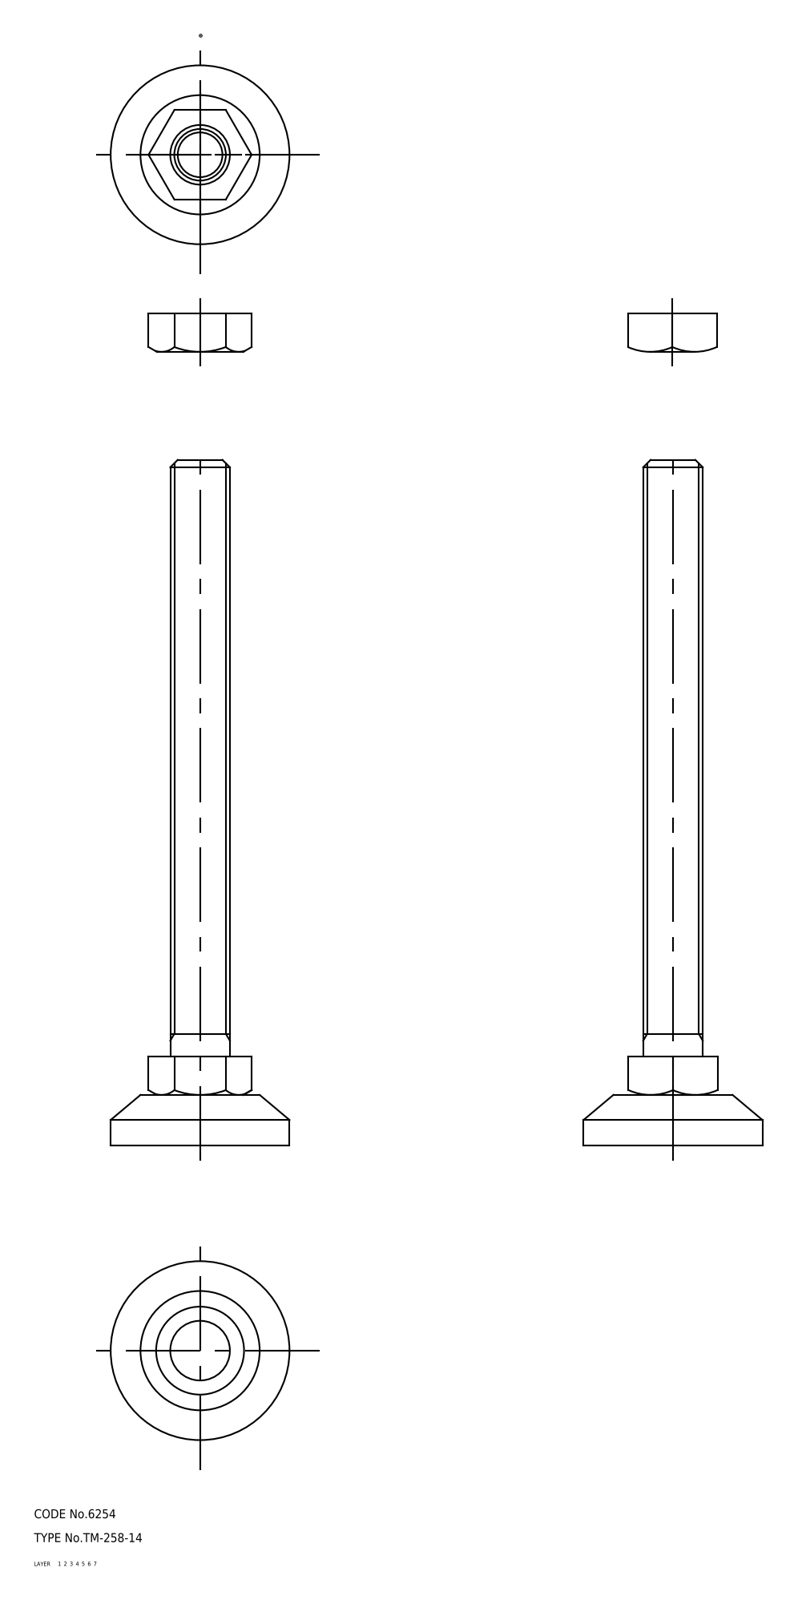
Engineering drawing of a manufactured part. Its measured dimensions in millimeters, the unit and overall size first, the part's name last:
Units: millimetres
Overall size (bounding box): 230 × 60 × 60
Volume: 111 487 mm³ · Surface area: 27 869 mm²
Bodies: 3 solids, 67 faces (0 planar, 0 cylindrical, 67 other)
Part name (STEP PRODUCT): 67112305; 67112318; 67112331
STEP written by: CADfix (AUTOMOTIVE_DESIGN)
